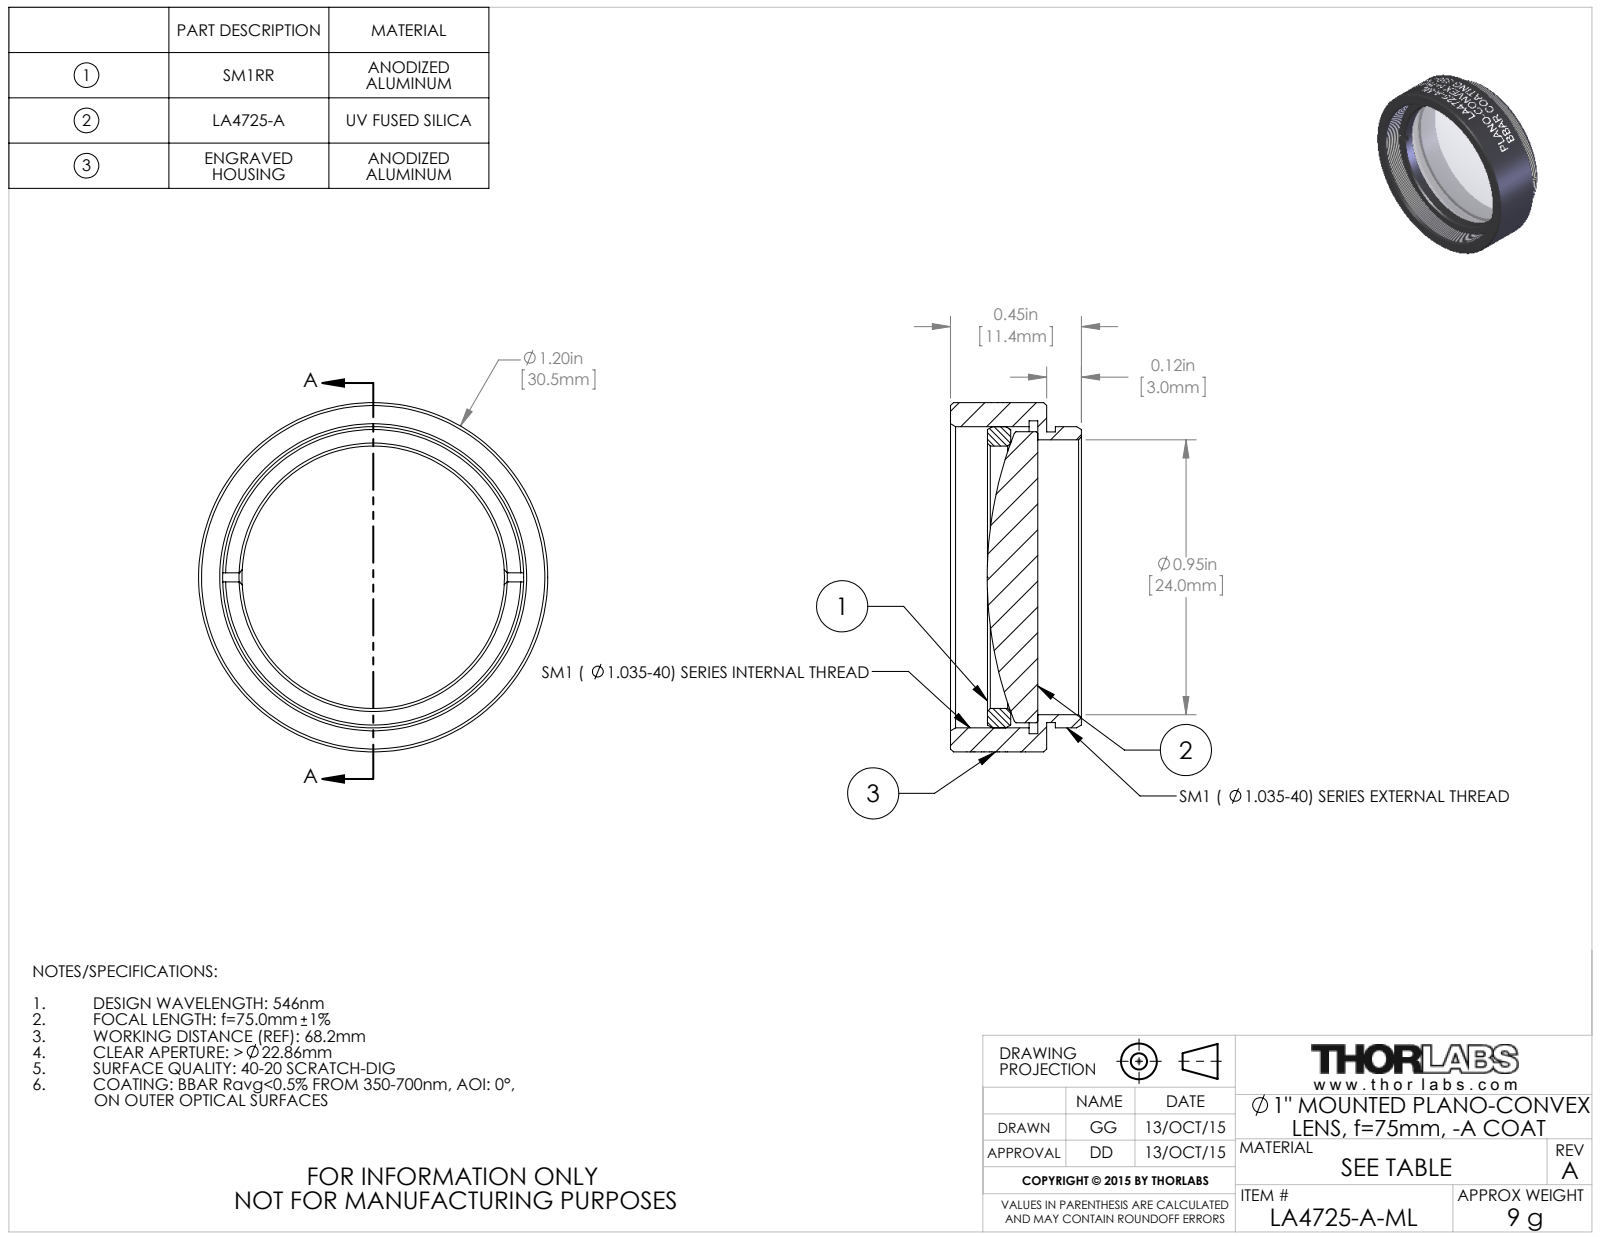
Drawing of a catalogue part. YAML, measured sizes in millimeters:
part_name: "TTN039360-E0W"
step_written_by: "SolidWorks 2014 (CONFIG_CONTROL_DESIGN)"
units: millimeters
bodies: {solids: 3, faces: 158, planar: 20, cylindrical: 110, other: 28}
overall_size: [30.48, 30.48, 11.43]
volume: 3714
surface_area: 4321
round_holes:
  - {diameter: 22.91, count: 1}
  - {diameter: 24, count: 1}
  - {diameter: 27.31, count: 1}
round_bosses_or_shafts:
  - {diameter: 30.48, count: 1}
  - {diameter: 26.29, count: 1}
  - {diameter: 25.4, count: 1}
  - {diameter: 25.37, count: 1}
face_to_face_distances: [0.76, 8.38, 7.62, 3.14, 2.38, 5.24, 5.17, 4.41, 2.03, 3.21]
